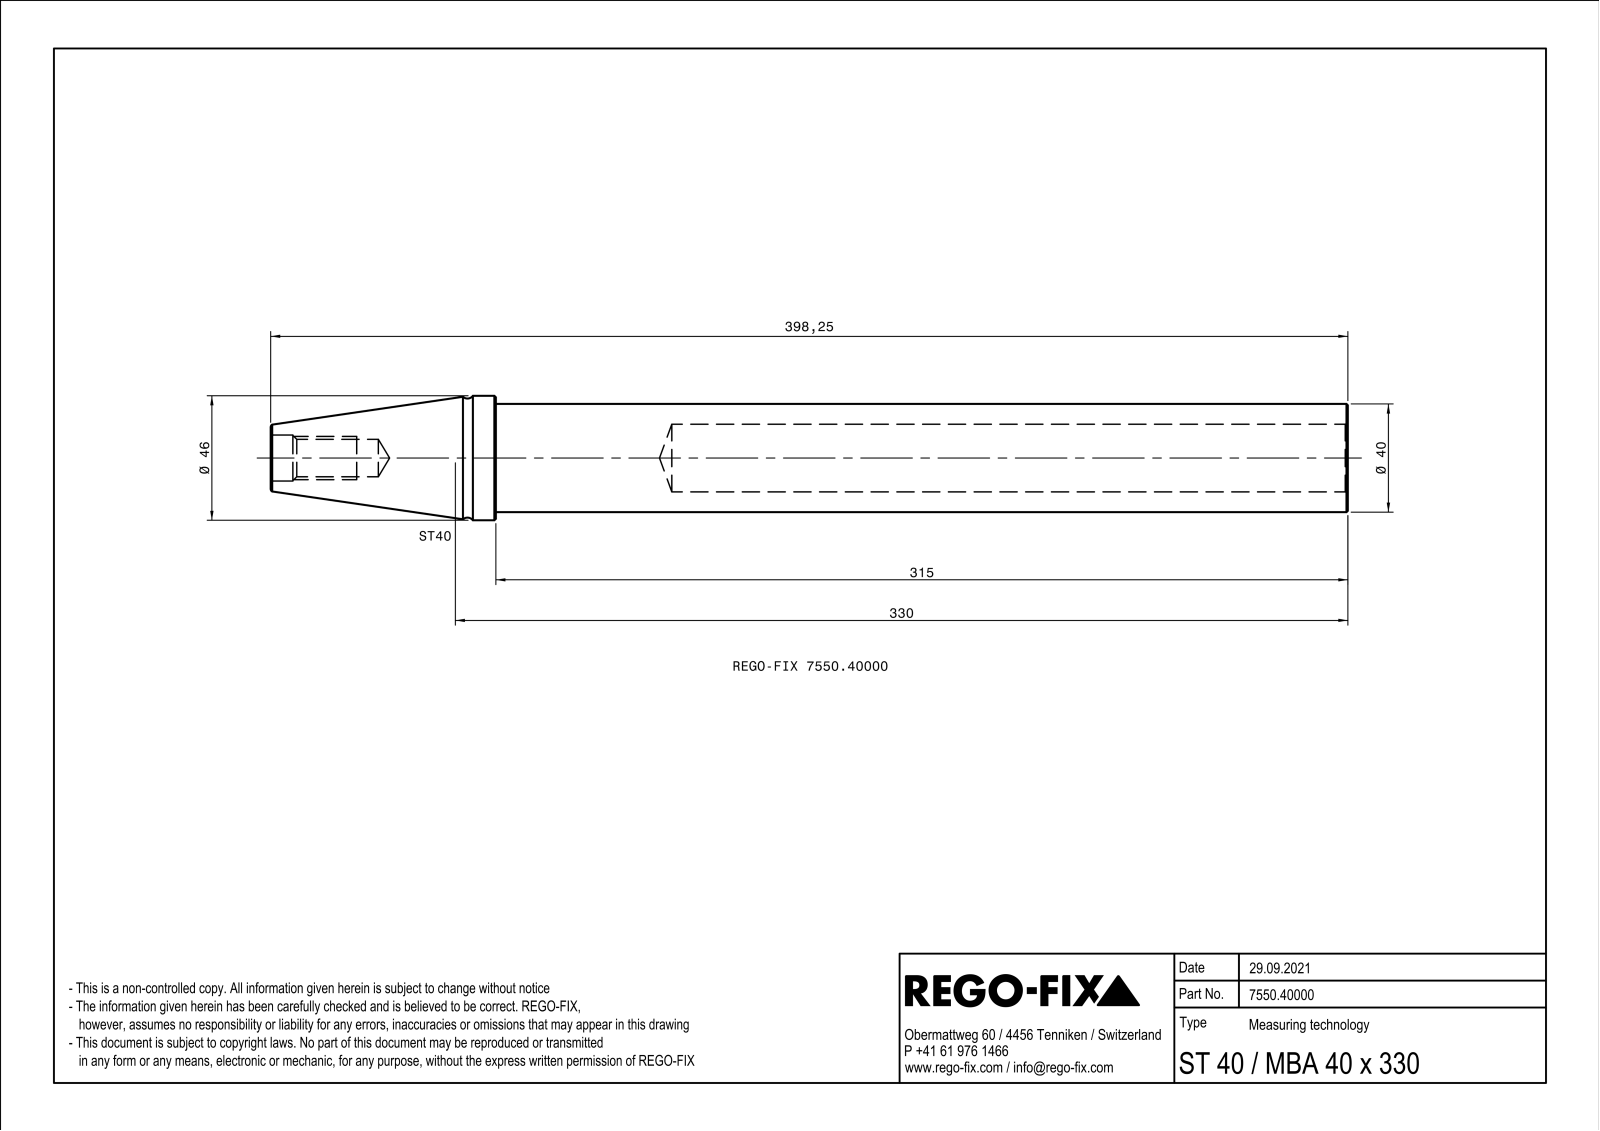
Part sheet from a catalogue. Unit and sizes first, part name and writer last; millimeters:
Units: millimetres
Overall size (bounding box): 398.25 × 46 × 46
Round holes (diameter × count): ⌀13.84 ×1, ⌀17 ×1, ⌀25 ×1
Round bosses / shafts (diameter × count): ⌀46 ×1, ⌀40 ×1, ⌀39.4 ×1
Main face-to-face distances: 315, 398.25, 83.25, 390.05, 75.05, 8.2
Volume: 355 161 mm³ · Surface area: 72 720 mm²
Bodies: 1 solid, 24 faces (4 planar, 6 cylindrical, 14 other)
Part name (STEP PRODUCT): NOCUT
STEP written by: SIEMENS PLM Software Solid Edge ST10 (AUTOMOTIVE_DESIGN)
